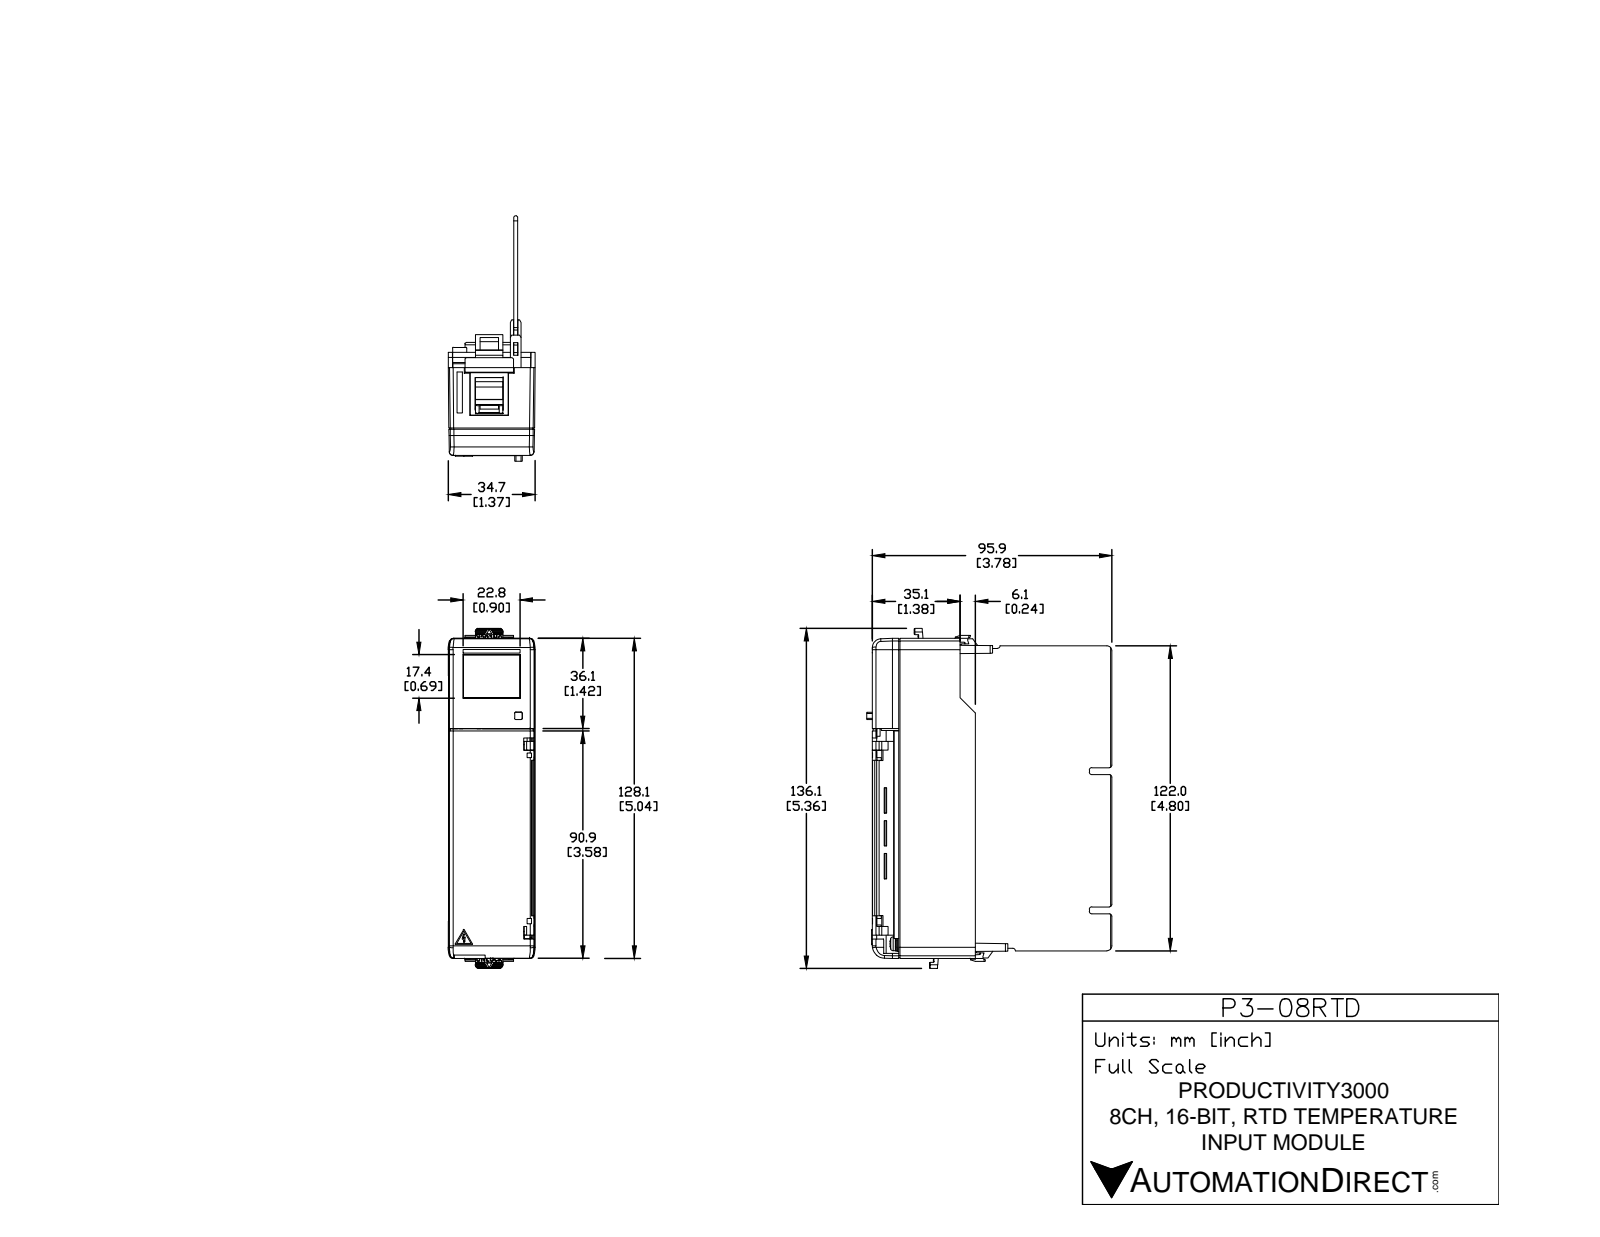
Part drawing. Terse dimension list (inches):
name: P3-08RTD
written by: SolidWorks 2009 (CONFIG_CONTROL_DESIGN)
unit: in
bodies: 1 solid, 3823 faces (2833 planar, 744 cylindrical, 246 other)
size: 5.357 × 3.865 × 1.37
volume: 6.185 in³; area: 116.8 in²
holes: 22× ⌀0.126, 2× ⌀0.197, 1× ⌀0.071
bosses: 22× ⌀0.217, 22× ⌀0.118, 20× ⌀0.094, 2× ⌀0.22, 2× ⌀0.087, 2× ⌀0.079, 1× ⌀0.059
rounds: 95× R0.02, 33× R0.039, 29× R0.012, 22× R0.066, 13× R0.059, 6× R0.079, 5× R0.008, 4× R0.004
face distances: 0.063, 0.067, 1.111, 1.044, 1.282, 0.874, 0.087, 0.311, 0.268, 0.209
hole spacings: 0.342, 0.3, 0.545, 0.6, 0.811, 0.9, 1.094, 1.2
